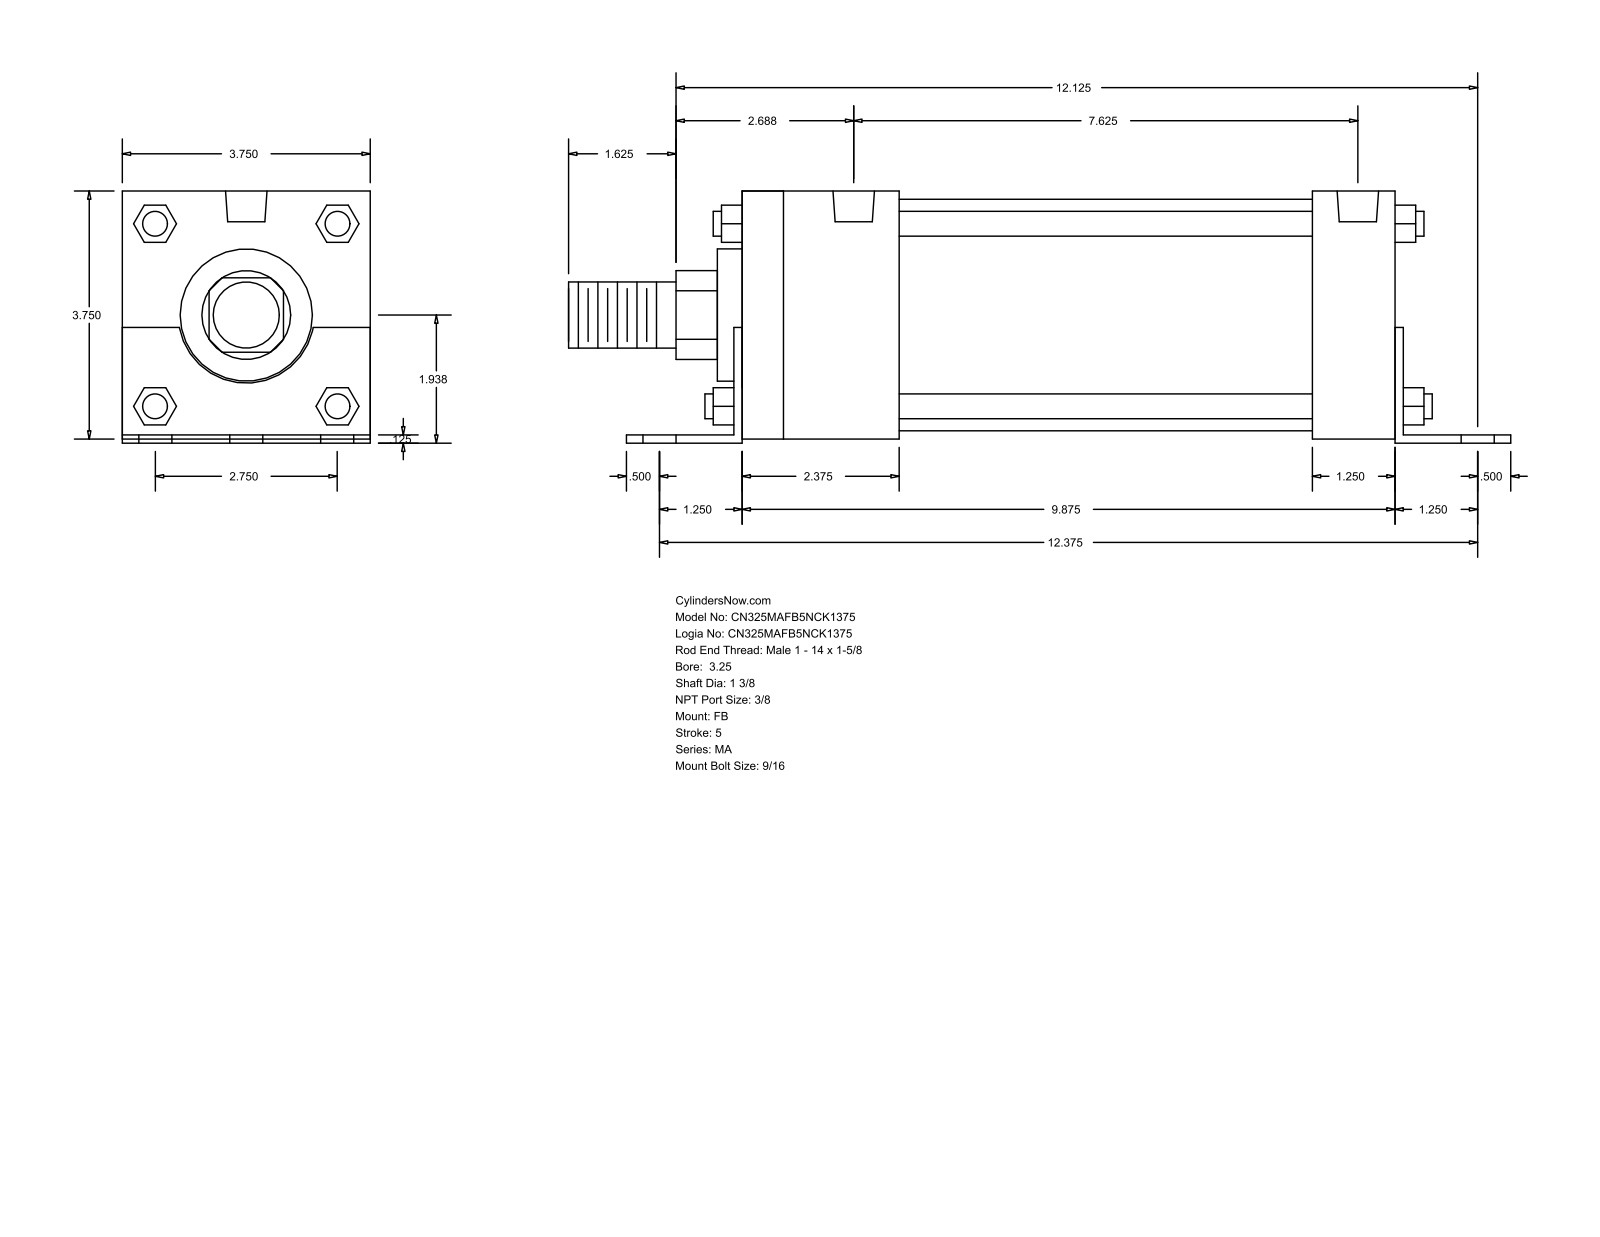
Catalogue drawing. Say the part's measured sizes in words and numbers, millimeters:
The part is named "MA_FB__0325_1.375". Its 3-D file was written by "GSSL Pune (CONFIG_CONTROL_DESIGN)". It is 0 solids with 140 faces: 105 planar, 35 cylindrical and 0 other. Overall it measures 361.95 by 96.84 by 95.25 millimeters. Round holes: 6 of diameter 14.29, 4 of diameter 11.11, 2 of diameter 15.93. Round bosses or shafts: 4 of diameter 9.53, 1 of diameter 88.9, 1 of diameter 50.8, 1 of diameter 34.92, 1 of diameter 25.4. Partial cylindrical surfaces (rounded edges, fillets, slot ends): 1 of radius 17.06, 1 of radius 26.16. The main face-to-face distances are 95.24, 3.17, 1.59, 96.83, 1.58, 93.66, 254, 250.83, 34.93, 257.17. The hole center spacings are 34.92, 316.26, 314.33, 57.78, 61.64, 69.84, 82.38, 86.72.
